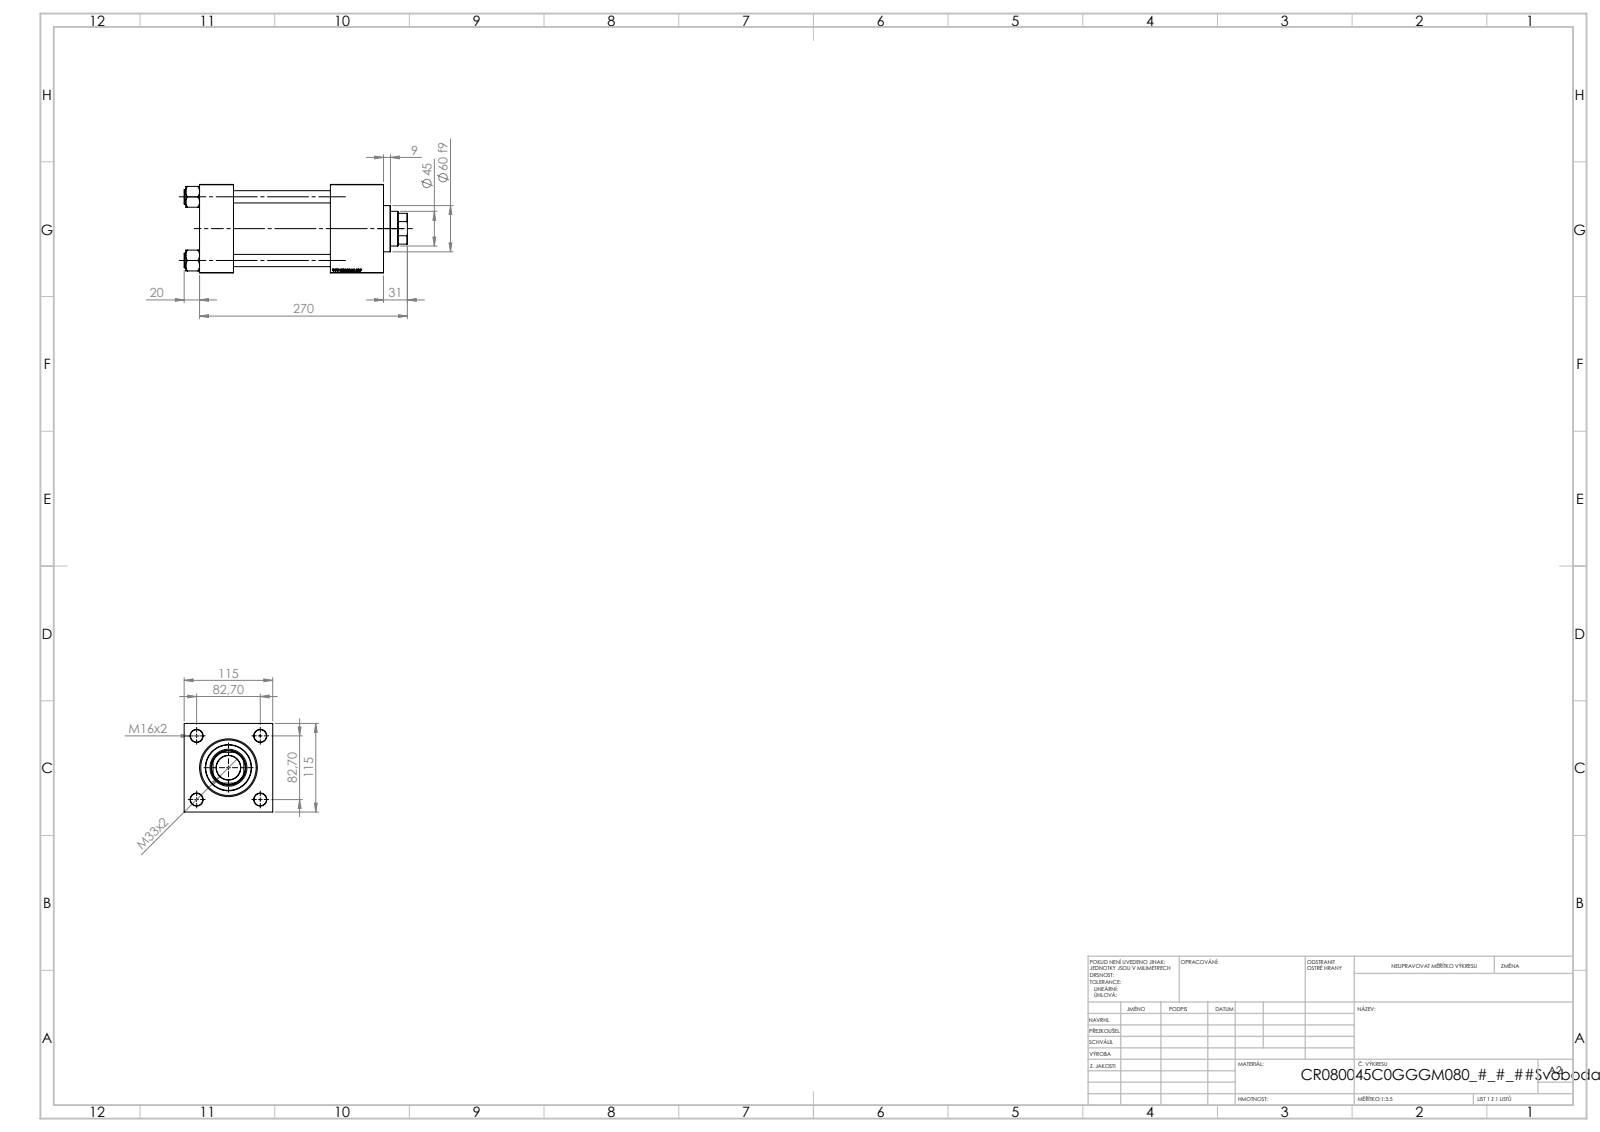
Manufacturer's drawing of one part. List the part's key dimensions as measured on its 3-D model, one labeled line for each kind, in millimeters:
Part name (STEP PRODUCT): V215CR_C_Body; V215CR_C_TYCINKA; NUT_M5_C; V215_VC_A (+1 more)
STEP written by: SolidWorks 2019 (CONFIG_CONTROL_DESIGN)
Units: millimetres
Bodies: 11 solids, 1197 faces (574 planar, 87 cylindrical, 536 other)
Overall size (bounding box): 290 × 115 × 115
Volume: 2 010 000 mm³ · Surface area: 325 721 mm²
Round holes (diameter × count): ⌀16 ×4, ⌀7 ×2, ⌀26.44 ×2, ⌀35 ×2, ⌀31.5 ×1, ⌀45 ×1, ⌀48 ×1, ⌀61 ×1, ⌀72 ×1, ⌀80 ×1
Round bosses / shafts (diameter × count): ⌀19 ×4, ⌀86 ×1, ⌀60 ×1
Partial cylindrical surfaces — rounded edges, fillets, slot ends (radius × count): R22 ×1
Main face-to-face distances: 115, 44, 239, 195, 170, 126, 69, 210.3, 166.3, 40.3
Hole centre spacings: 58.48, 82.7, 116.96, 171
